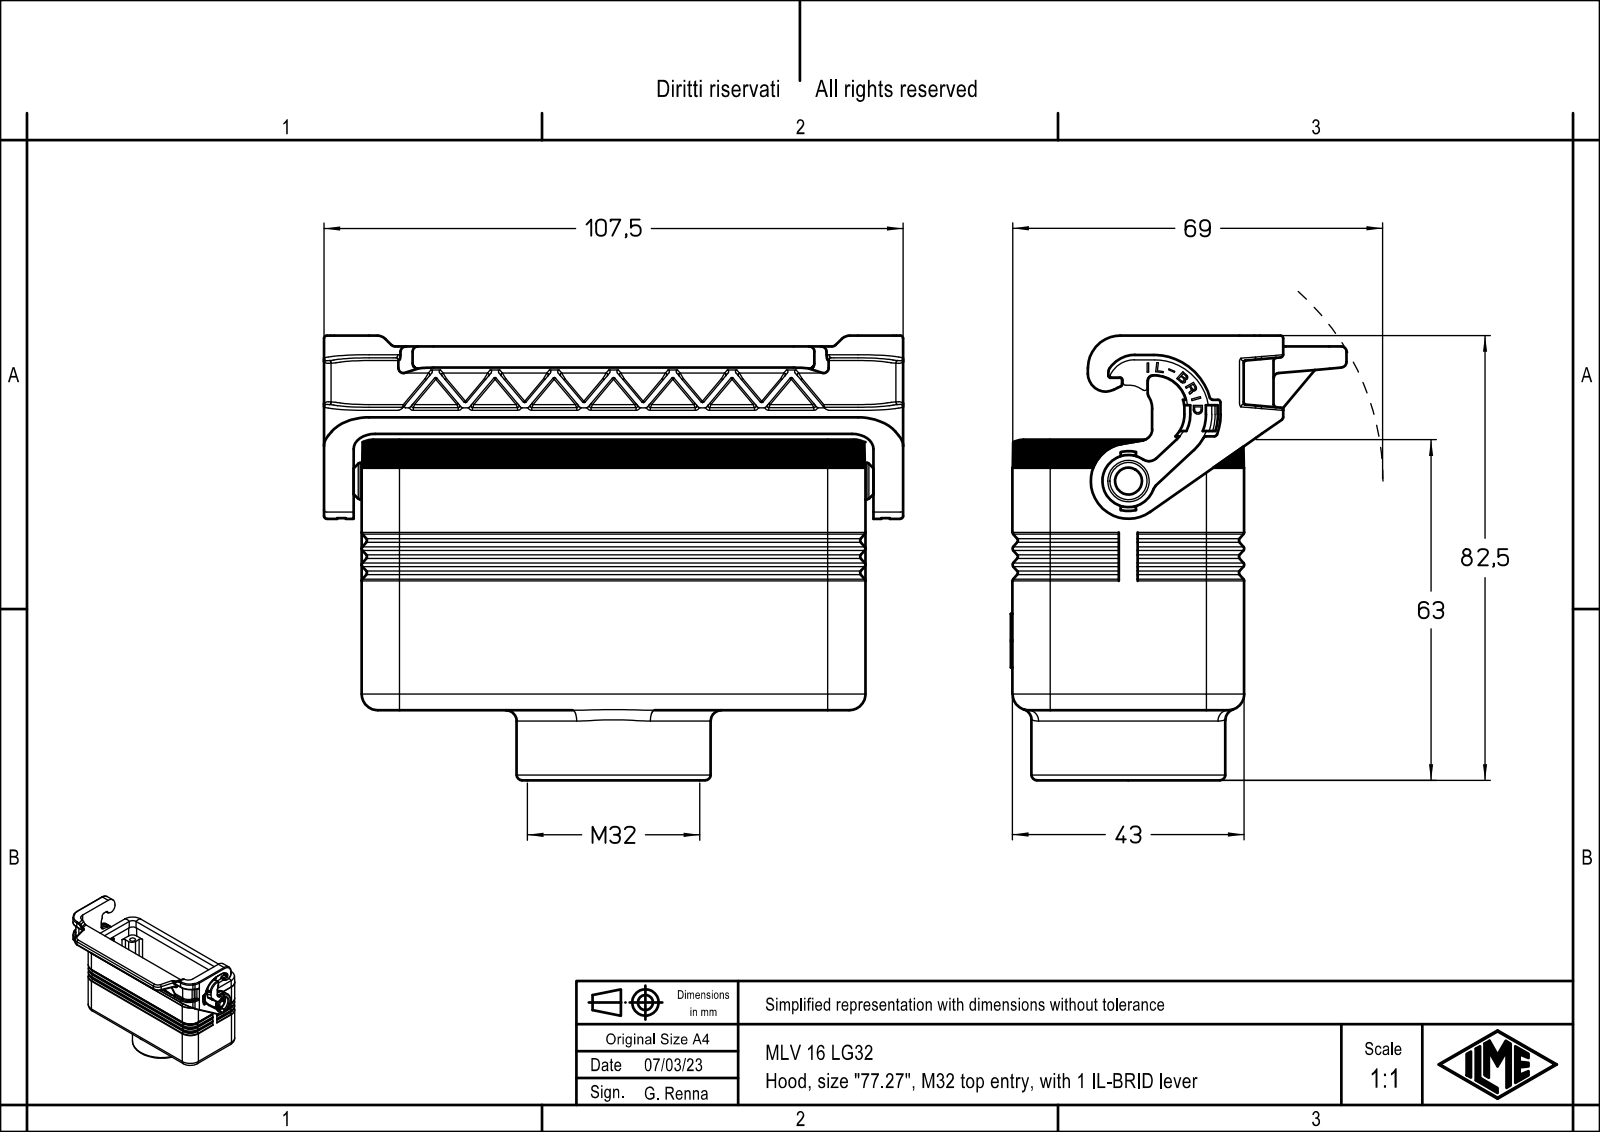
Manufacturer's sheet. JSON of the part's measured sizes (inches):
{"part_name": "MLV 16 LG32", "step_written_by": "Creo Elements/Direct Modeling 20.1B 02-Apr-2019 (C) Parametric Technology GmbH (AUTOMOTIVE_DESIGN)", "units": "inches", "bodies": {"solids": 1, "faces": 1159, "planar": 685, "cylindrical": 314, "other": 160}, "overall_size": [4.232, 3.248, 2.453], "volume_in3": 4.689, "surface_area_in2": 74.73, "round_holes": [[0.118, 4], [0.138, 4], [0.128, 1], [0.213, 1], [0.303, 1], [1.102, 1], [1.205, 1]], "round_bosses_or_shafts": [[1.417, 1], [0.272, 1], [0.268, 1], [0.205, 1], [0.126, 1]], "partial_cylinders_radius": [[0.02, 31], [0.004, 27], [0.008, 15], [0.013, 15], [0.039, 15], [0.118, 12], [0.276, 10], [0.059, 9]], "face_to_face_distances": [0.138, 1.555, 1.417, 1.693, 0.11, 1.821, 0.128, 0.266, 1.683, 0.059], "hole_center_spacings": [1.615, 1.063, 3.051, 3.231]}
